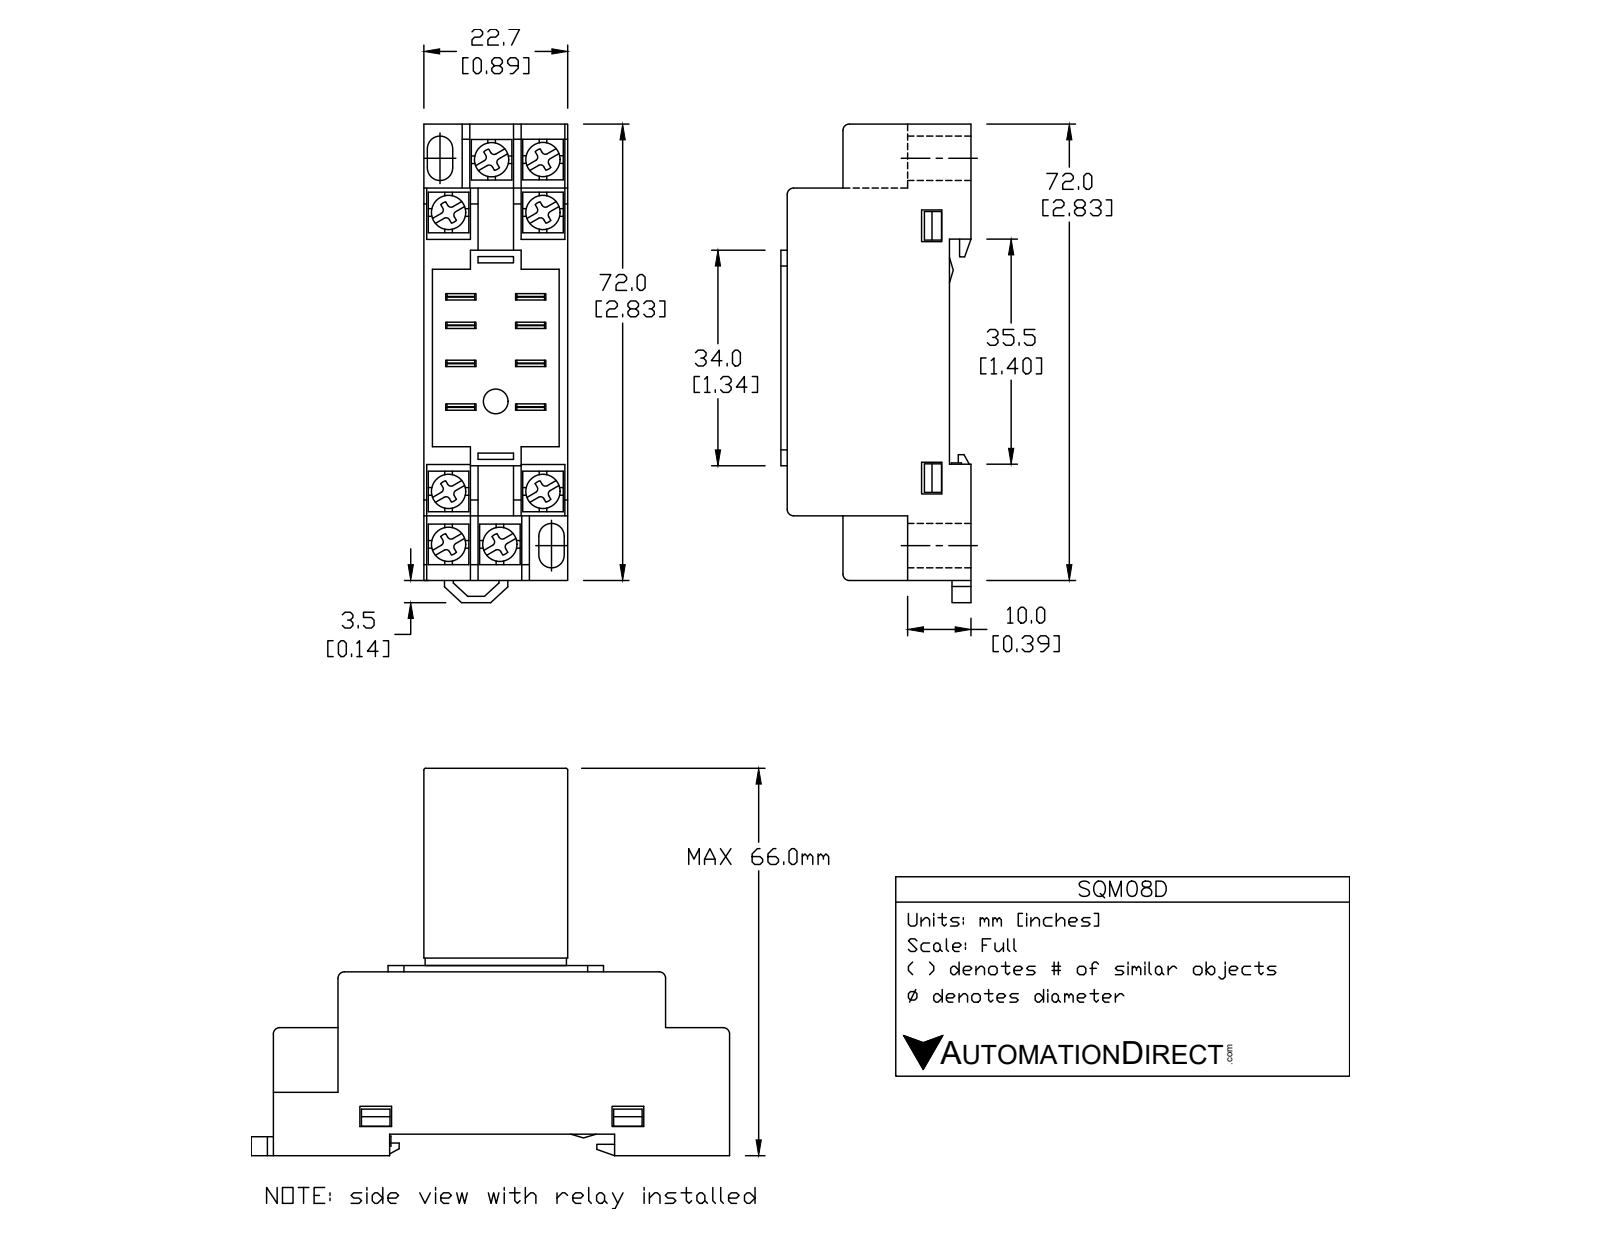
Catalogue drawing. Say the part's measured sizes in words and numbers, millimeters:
The part is named "SQM08D". Its 3-D file was written by "SolidWorks 2013 (AUTOMOTIVE_DESIGN)". It is 2 solids with 400 faces: 358 planar, 26 cylindrical and 16 other. Overall it measures 75.1 by 30 by 22.7 millimeters. Its volume is 35 626 cubic millimeters and its surface area 11 206 square millimeters. Round holes: 1 of diameter 3.9. Round bosses or shafts: 8 of diameter 6. Partial cylindrical surfaces (rounded edges, fillets, slot ends): 8 of radius 1.5. The main face-to-face distances are 22.7, 3.5, 30, 26.5, 9.5, 62.4, 6.15, 14.75, 0.5, 7.15.
